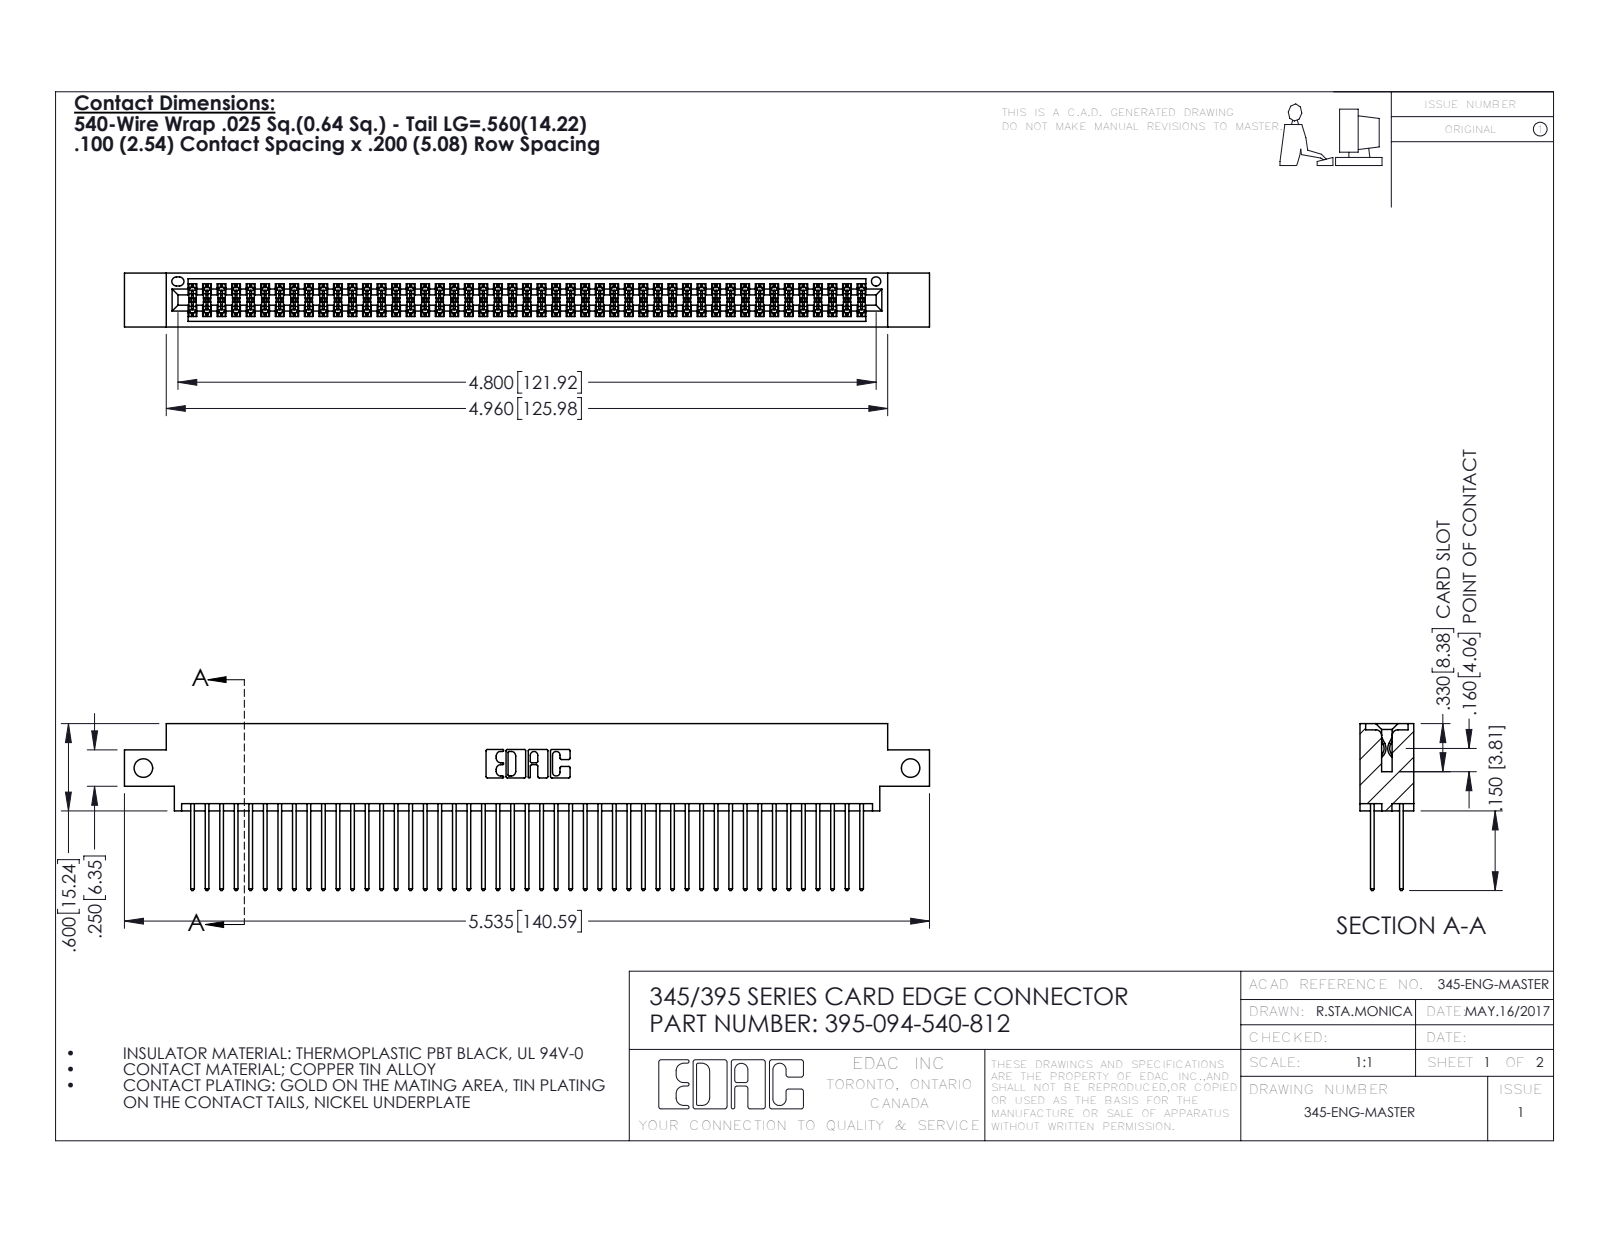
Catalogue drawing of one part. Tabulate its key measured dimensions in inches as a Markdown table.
| quantity | value |
| --- | --- |
| part name | 345 Part_0.170 Offset - Side Mount; 345-292-001_345-293-140; 395-094-540-812 |
| STEP written by | SolidWorks 2016 (CONFIG_CONTROL_DESIGN) |
| units | inches |
| bodies | 95 solids, 4830 faces (3186 planar, 1644 cylindrical, 0 other) |
| overall size | 5.535 × 1.147 × 0.37 |
| volume | 0.846 in³ |
| surface area | 34.48 in² |
| round holes (diameter × count) | 0.128 × 2, 0.064 × 1 |
| partial cylindrical surfaces (radius × count) | 0.006 × 141, 0.01 × 94, 0.01 × 22, 0.007 × 6, 0.031 × 6, 0.026 × 3, 0.014 × 2, 0.019 × 2 |
| main face-to-face distances | 0.298, 0.072, 0.2, 0.098, 0.272, 0.025, 0.37, 0.225, 0.175, 0.149 |
| hole center spacings | 5.275 |
